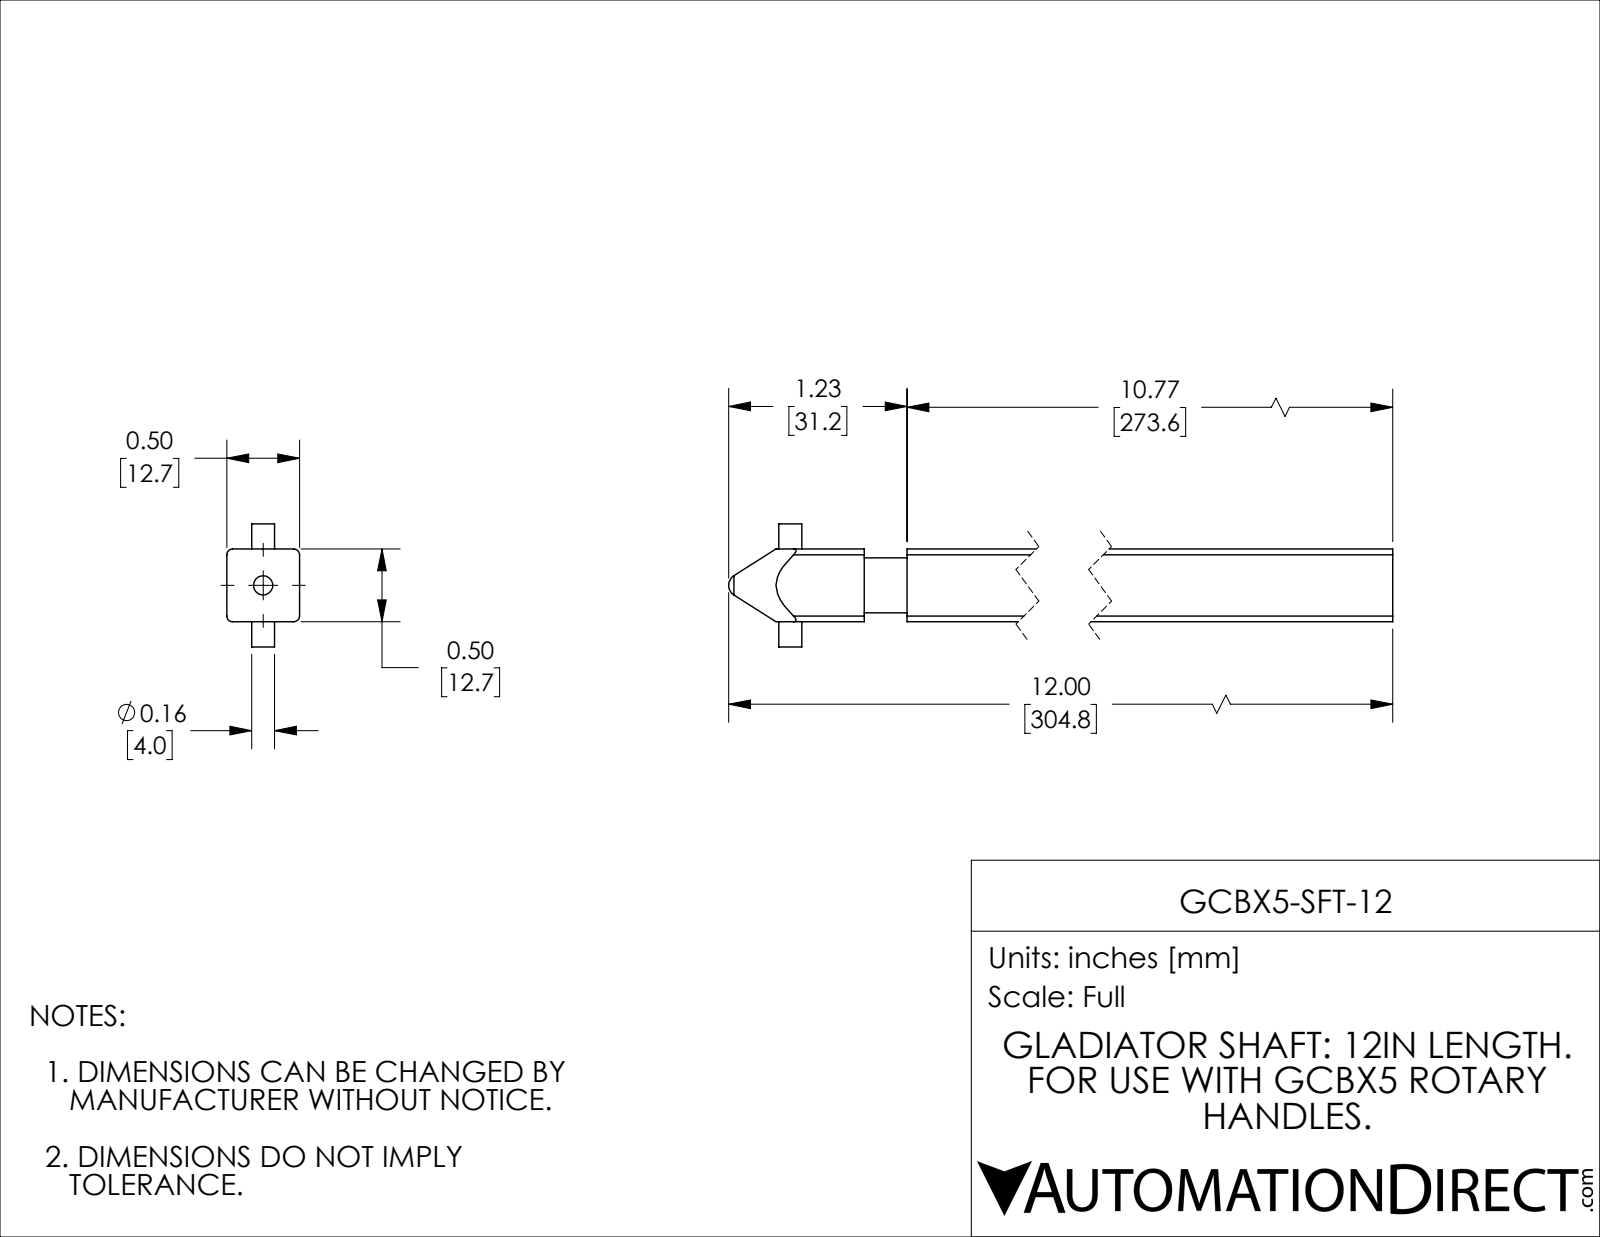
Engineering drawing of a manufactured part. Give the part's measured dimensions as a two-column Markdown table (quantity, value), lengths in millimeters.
| quantity | value |
| --- | --- |
| part name | GCBX5-SFT-12 |
| STEP written by | SolidWorks 2021 (CONFIG_CONTROL_DESIGN) |
| units | millimeters |
| bodies | 1 solid, 39 faces (15 planar, 17 cylindrical, 7 other) |
| overall size | 304.8 × 21.5 × 12.7 |
| volume | 47 180 mm³ |
| surface area | 15 330 mm² |
| round holes (diameter × count) | 3.6 × 1 |
| round bosses / shafts (diameter × count) | 9.6 × 1, 4 × 1 |
| partial cylindrical surfaces (radius × count) | 1 × 4 |
| main face-to-face distances | 12.7, 273.6, 281.1, 7.5, 6.2, 6.5, 4.4, 17.1, 21.5 |
